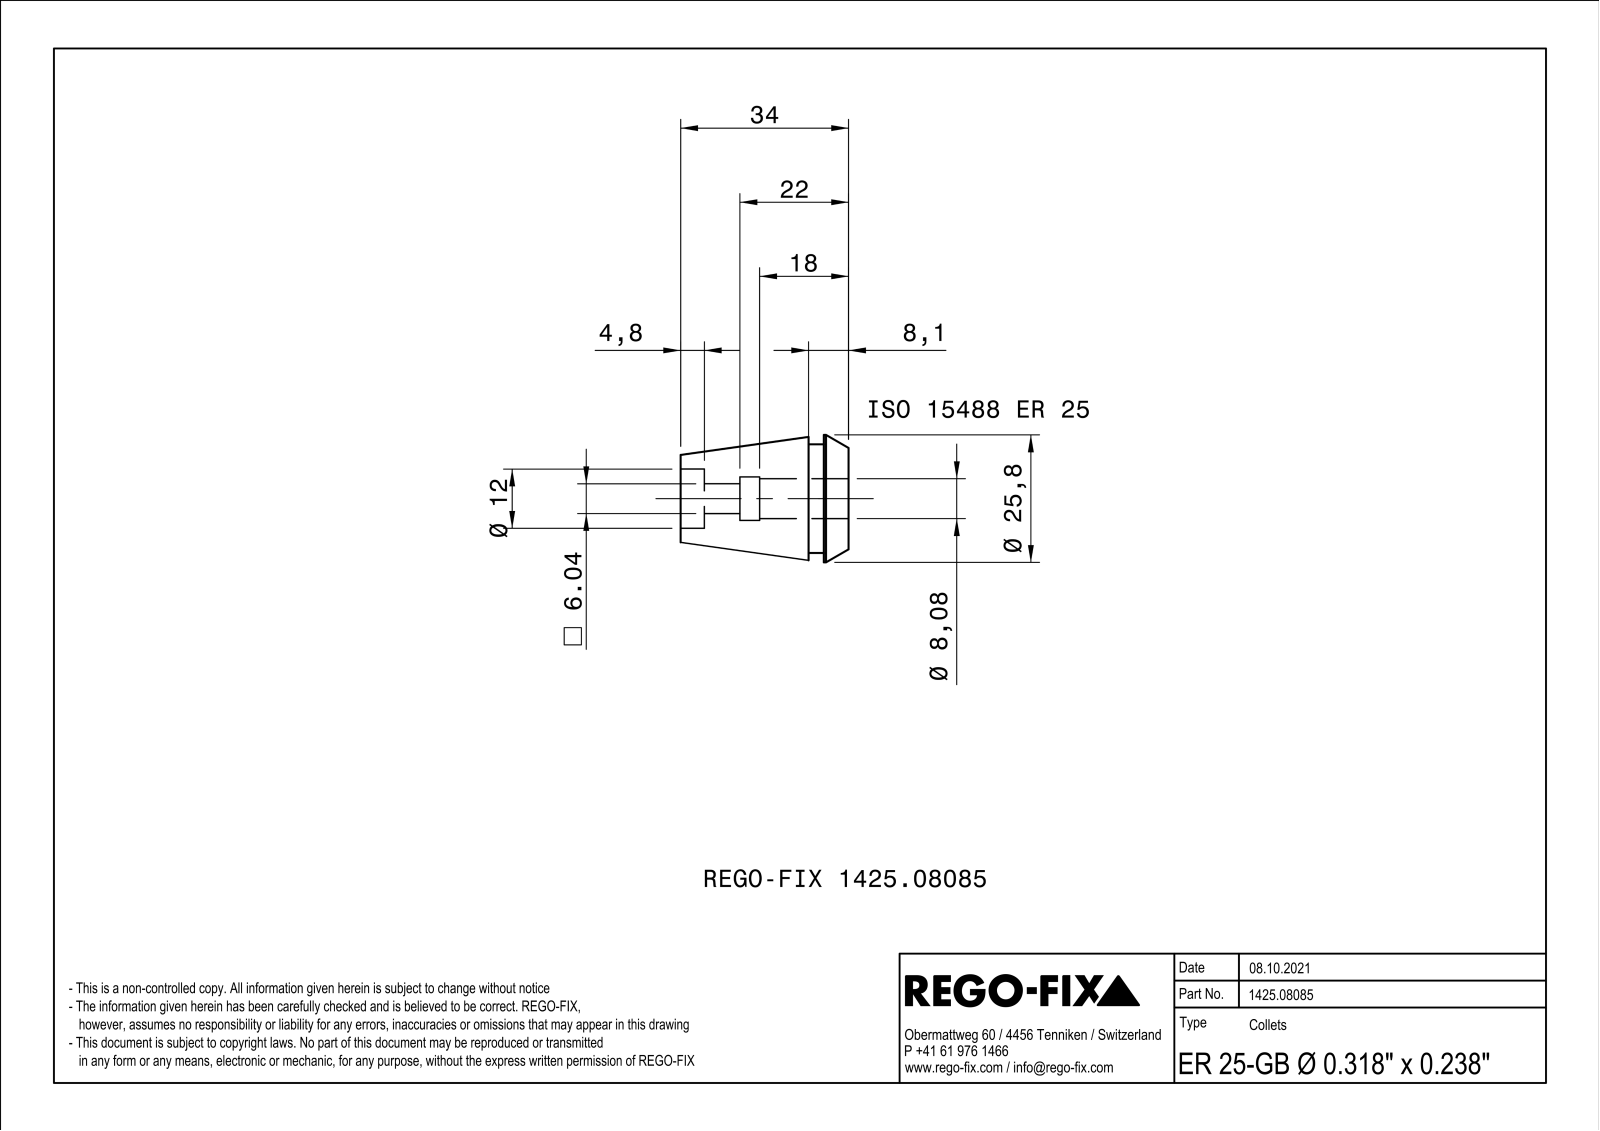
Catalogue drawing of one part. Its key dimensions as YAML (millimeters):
part_name: "NOCUT"
step_written_by: "SIEMENS PLM Software Solid Edge ST10 (AUTOMOTIVE_DESIGN)"
units: millimeters
bodies: {solids: 1, faces: 152, planar: 68, cylindrical: 32, other: 52}
overall_size: [34, 25.79, 25.79]
volume: 9415
surface_area: 6777
round_holes:
  - {diameter: 8.08, count: 1}
  - {diameter: 12, count: 1}
round_bosses_or_shafts:
  - {diameter: 25.8, count: 1}
  - {diameter: 22, count: 1}
partial_cylinders:
  - {radius: 3.6, count: 1}
  - {radius: 4.4, count: 1}
face_to_face_distances: [0.8, 5, 34, 29, 8.1, 3.1, 25.9, 2.85, 3.65, 6.5]
